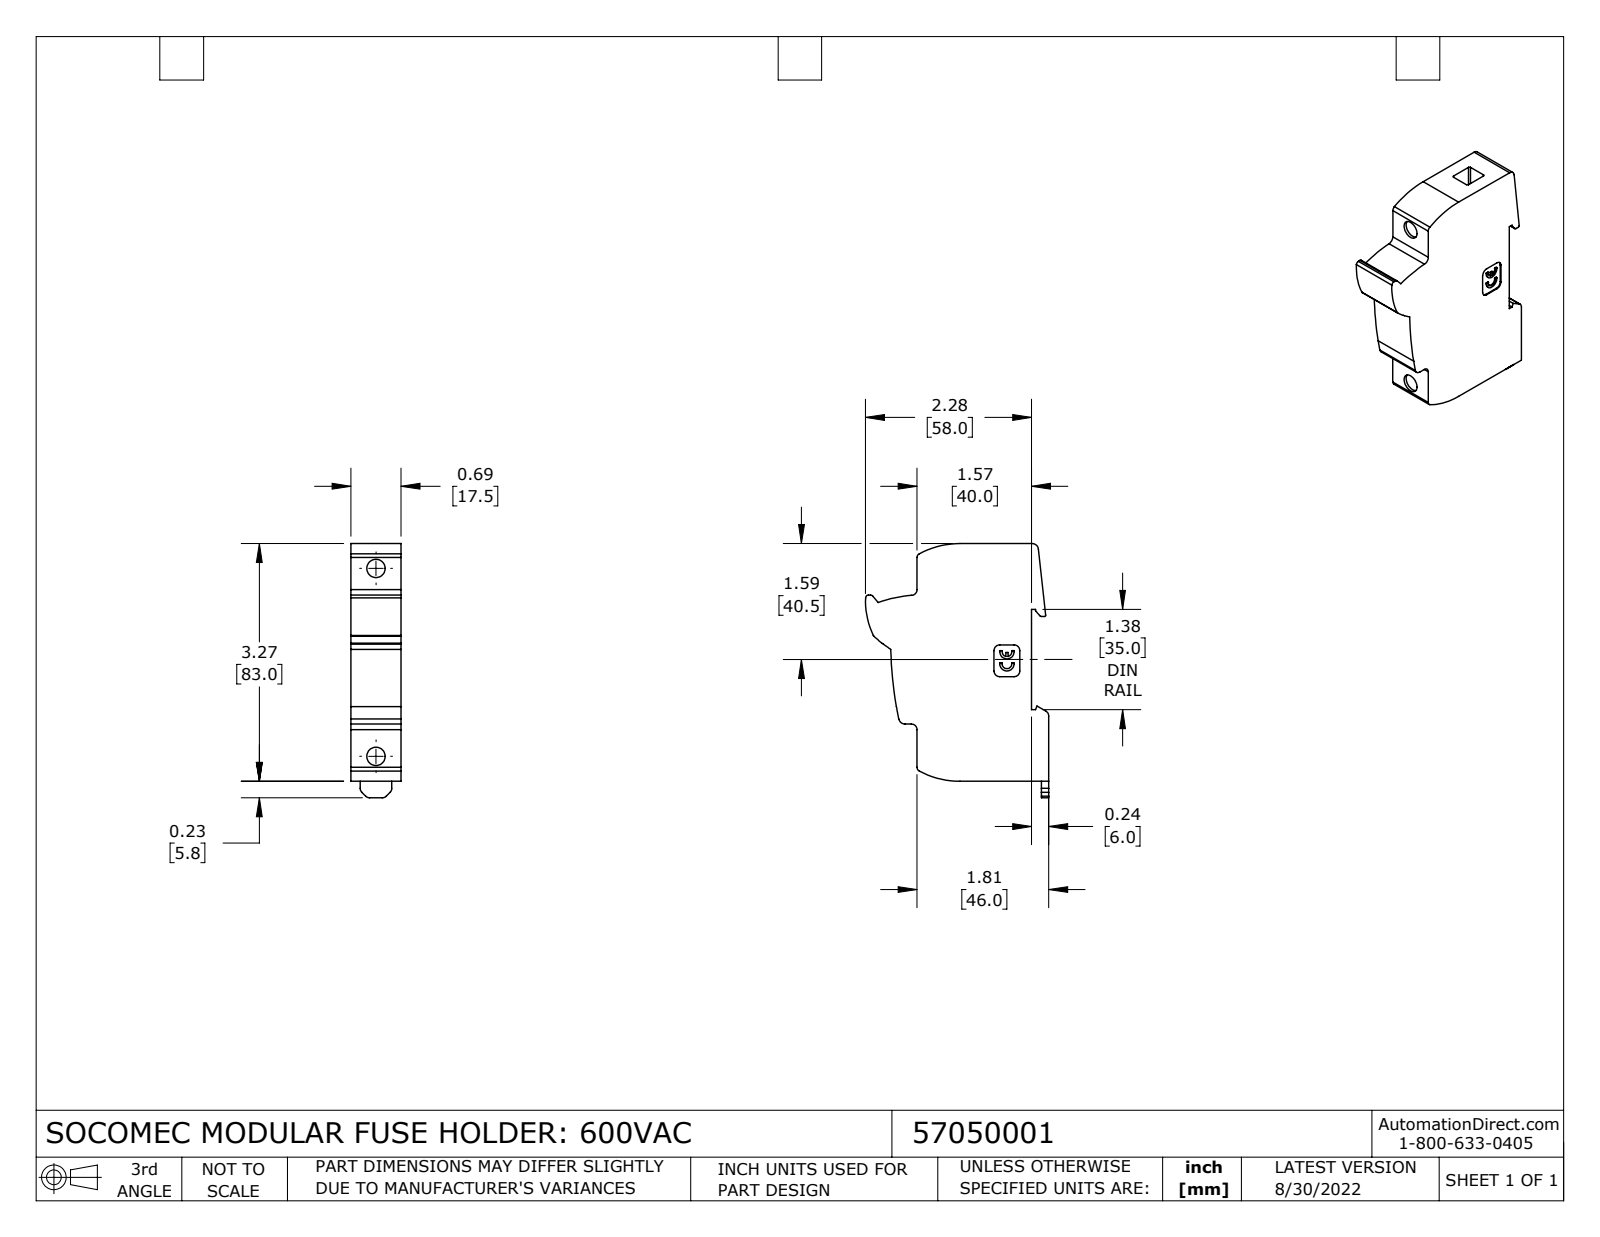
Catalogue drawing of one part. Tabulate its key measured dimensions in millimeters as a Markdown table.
| quantity | value |
| --- | --- |
| part name | 57050001 |
| STEP written by | SolidWorks 2021 (CONFIG_CONTROL_DESIGN) |
| units | millimeters |
| bodies | 1 solid, 105 faces (52 planar, 53 cylindrical, 0 other) |
| overall size | 88.8 × 64 × 17.5 |
| volume | 69 300 mm³ |
| surface area | 13 760 mm² |
| round holes (diameter × count) | 6.4 × 2 |
| partial cylindrical surfaces (radius × count) | 2 × 11, 0.5 × 5, 1 × 4, 1.5 × 2, 1.7 × 2, 2.2 × 2, 2.5 × 2, 30.1 × 2 |
| main face-to-face distances | 17.5, 6, 40, 83, 46, 5.1, 12.4, 7.4, 13.2, 7.1 |
| hole center spacings | 65.6 |
